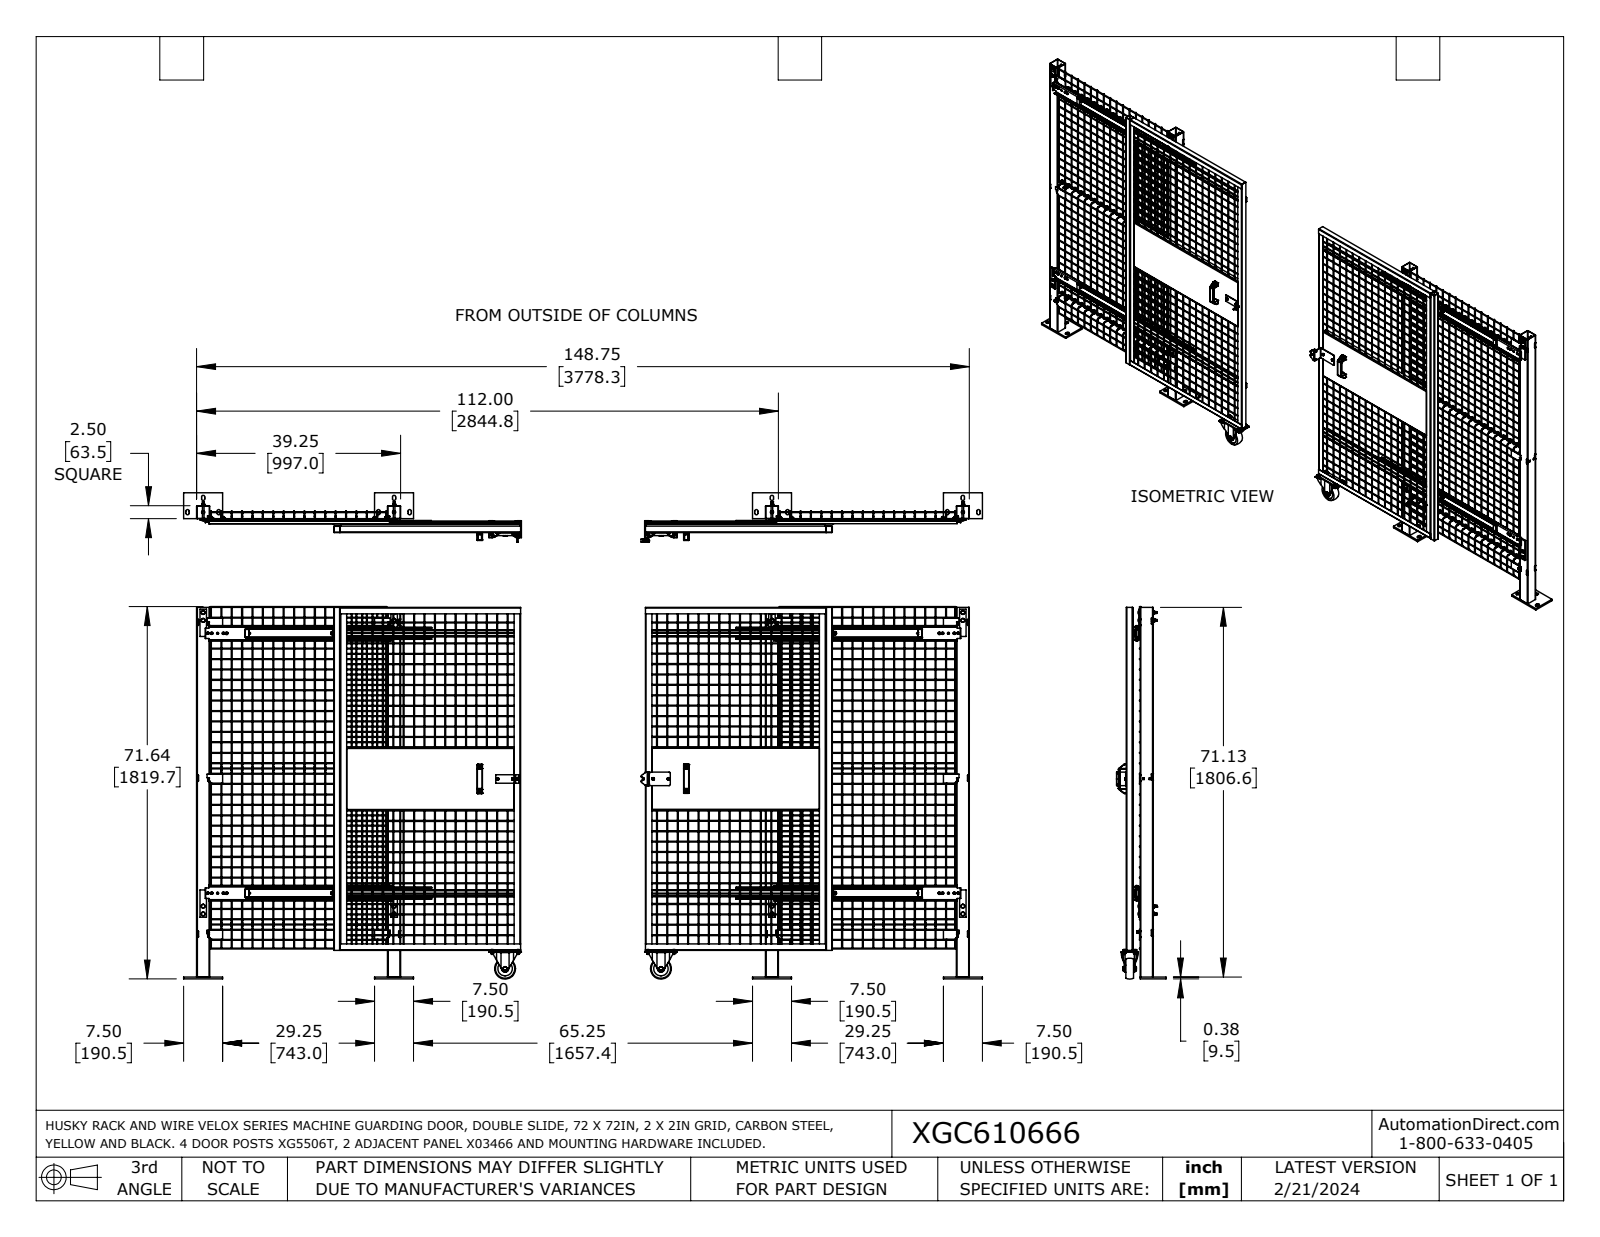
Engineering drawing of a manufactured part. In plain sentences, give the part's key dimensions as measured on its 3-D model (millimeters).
The part is named "XGC610666_REV3". Its 3-D file was written by "SolidWorks 2023 (AUTOMOTIVE_DESIGN)". It is 294 solids with 6898 faces: 3181 planar, 2100 cylindrical and 1617 other. Overall it measures 3905.3 by 1820.2 by 242.4 millimeters. Its volume is 13 290 000 cubic millimeters and its surface area 12 720 000 square millimeters. Round holes: 28 of diameter 5.2, 28 of diameter 7.4, 16 of diameter 3.5, 16 of diameter 4.6, 16 of diameter 6.1, 13 of diameter 6.4, 12 of diameter 4.7, 12 of diameter 7.1, 12 of diameter 7.6, 12 of diameter 8.7, 8 of diameter 8, 4 of diameter 5.1. Round bosses or shafts: 324 of diameter 4.1, 93 of diameter 4.2, 16 of diameter 17.4, 16 of diameter 15.1, 16 of diameter 12.7, 16 of diameter 10.4, 16 of diameter 8, 16 of diameter 6.4. Partial cylindrical surfaces (rounded edges, fillets, slot ends): 96 of radius 0.2, 56 of radius 1.3, 55 of radius 3.3, 32 of radius 1.6, 32 of radius 3.4, 32 of radius 4.4, 28 of radius 1.5, 28 of radius 2.6. The main face-to-face distances are 1.5, 62, 63.5, 933.5, 2781.3, 60.6, 66, 64.2, 1.8, 127.7. The hole center spacings are 127, 63.5, 50.8, 136.8, 209.6, 254, 762, 763.7.
